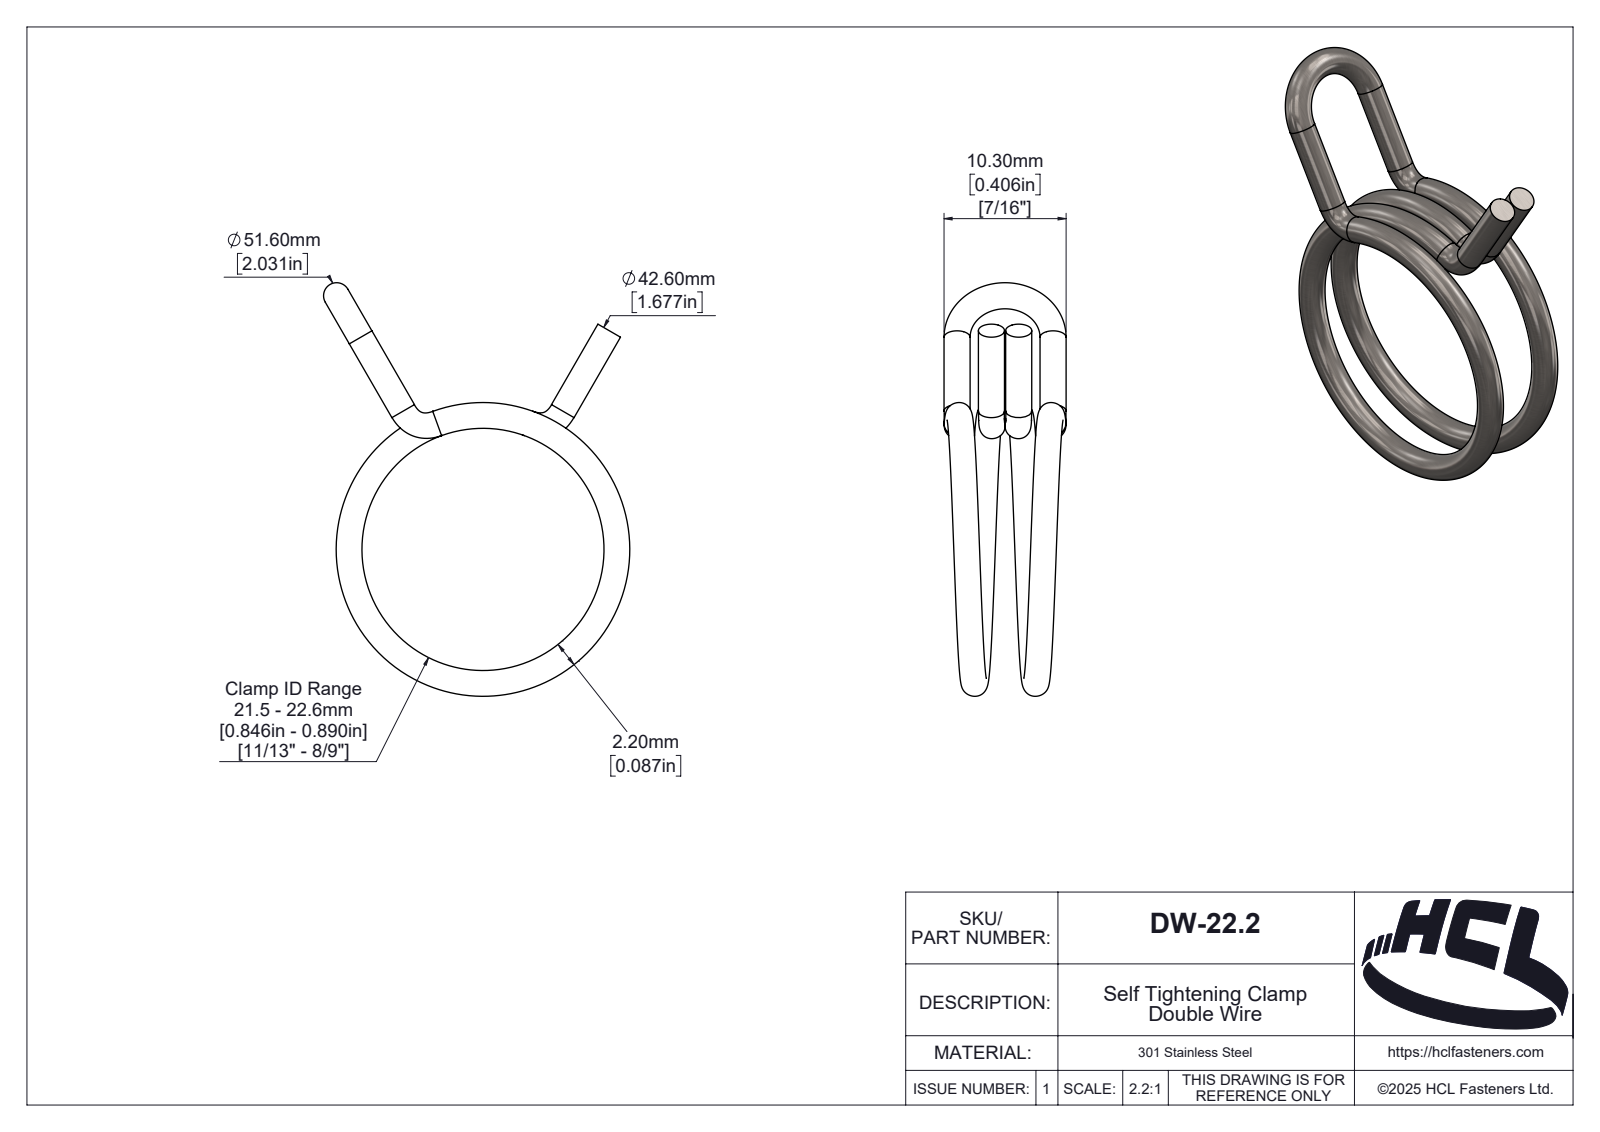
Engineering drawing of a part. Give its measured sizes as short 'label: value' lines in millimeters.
name: DW-21.2
written by: SolidWorks 2025 (AUTOMOTIVE_DESIGN)
unit: mm
bodies: 1 solid, 132 faces (14 planar, 53 cylindrical, 65 other)
size: 33.57 × 24.79 × 10.3
volume: 636 mm³; area: 1 287 mm²
bosses: 4× ⌀2
rounds: 1× R0.16, 1× R0.2, 1× R0.21, 1× R0.26, 1× R0.36, 1× R0.48, 1× R0.6, 1× R0.68
